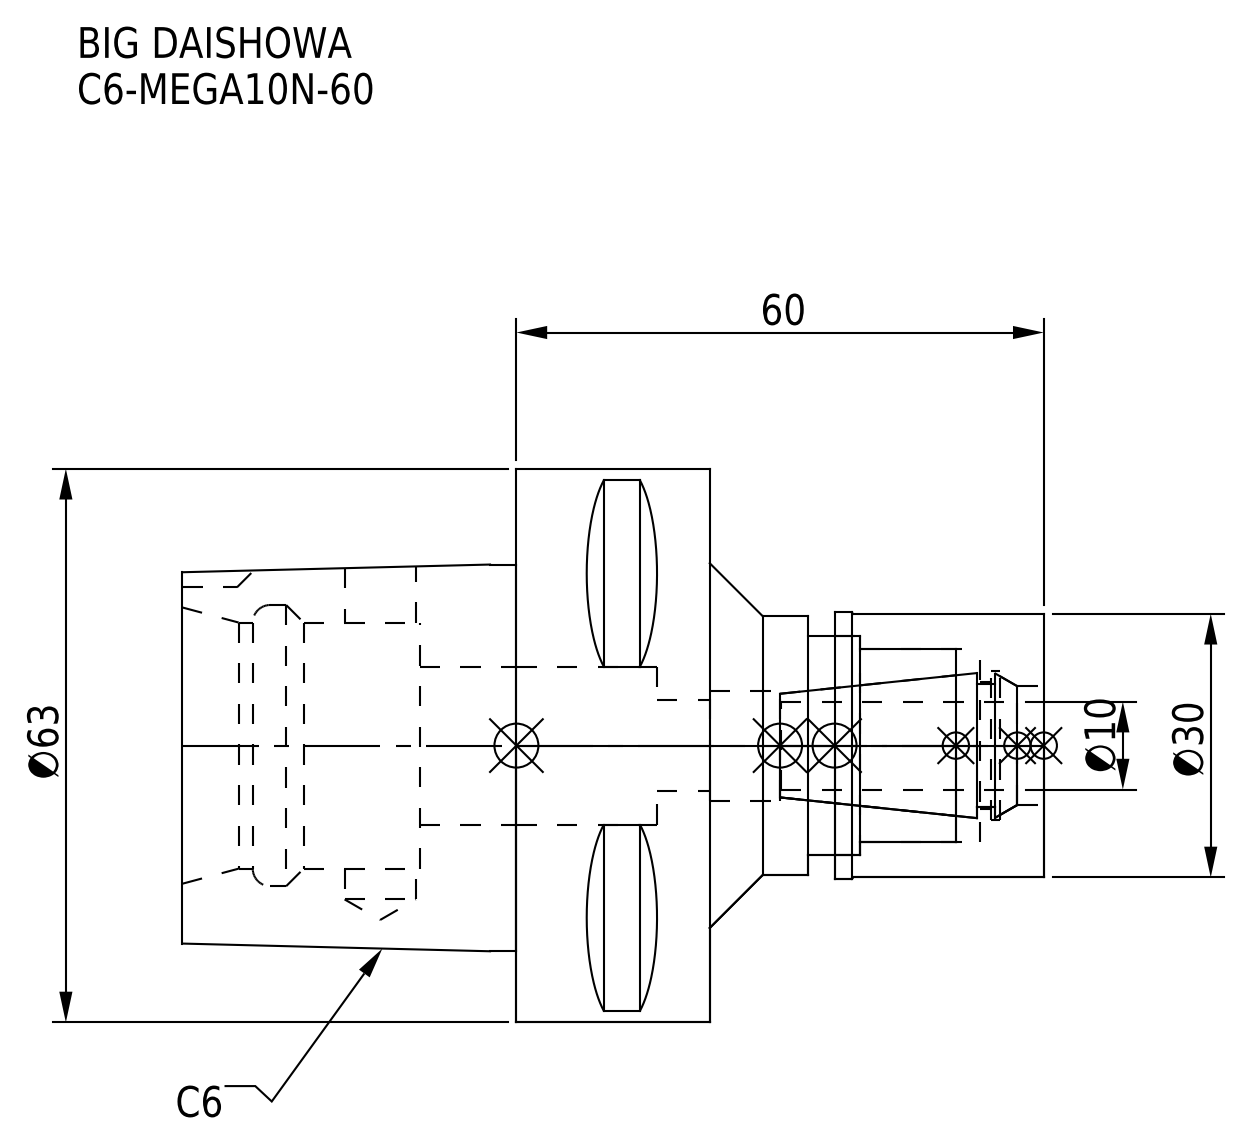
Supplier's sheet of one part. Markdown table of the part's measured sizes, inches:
| quantity | value |
| --- | --- |
| part name | DXF_TEMP_ASSY_ASM_4_ASM.stp; MGN10_1.stp; C6-MEGA10N-60; C6-MEGA10N-60-100_ASM.stp (+3 more) |
| STEP written by | SolidWorks 2019 (CONFIG_CONTROL_DESIGN) |
| units | inches |
| bodies | 2 solids, 95 faces (38 planar, 39 cylindrical, 18 other) |
| overall size | 3.858 × 2.48 × 2.48 |
| volume | 7.18 in³ |
| surface area | 43.79 in² |
| round holes (diameter × count) | 0.319 × 1, 0.409 × 1, 0.492 × 1, 0.531 × 1, 0.571 × 1, 0.669 × 1, 0.709 × 1, 0.866 × 1, 0.984 × 1, 1.102 × 1, 1.26 × 1 |
| round bosses / shafts (diameter × count) | 2.48 × 1, 1.193 × 1, 1.181 × 1, 1.161 × 1 |
| partial cylindrical surfaces (radius × count) | 0.197 × 1 |
| main face-to-face distances | 0.866, 1.496, 2.362, 1.063, 3.858, 1.299, 2.795, 0.433, 0.98, 2.181 |
